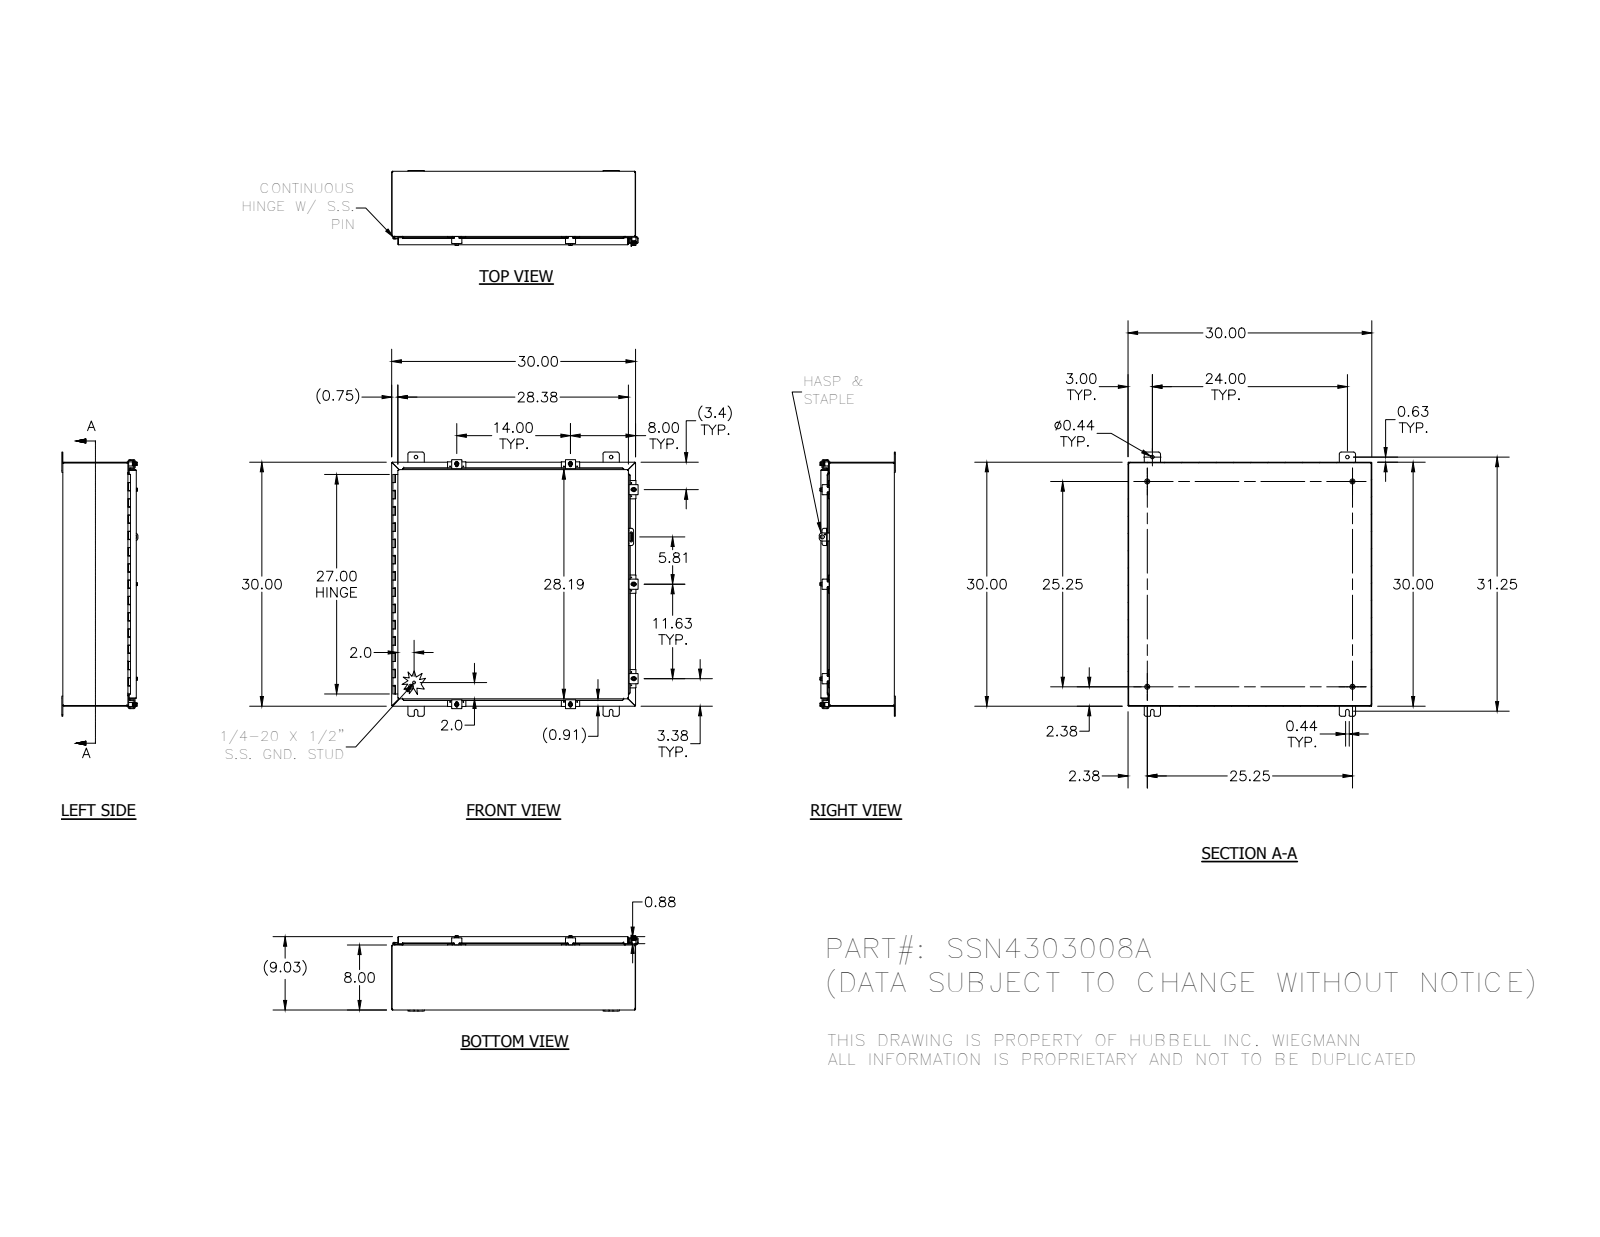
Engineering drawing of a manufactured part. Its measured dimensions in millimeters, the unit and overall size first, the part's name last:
Units: millimetres
Overall size (bounding box): 825.5 × 767.5 × 237.6
Round holes (diameter × count): ⌀2.8 ×14, ⌀5.4 ×7, ⌀7.1 ×7, ⌀7.6 ×7, ⌀11.1 ×4, ⌀3.2 ×1, ⌀4 ×1, ⌀12.7 ×1
Round bosses / shafts (diameter × count): ⌀6.4 ×9, ⌀13.2 ×7, ⌀12.7 ×7, ⌀8.9 ×7, ⌀15.9 ×4, ⌀8.4 ×4, ⌀8.6 ×1, ⌀3 ×1
Partial cylindrical surfaces — rounded edges, fillets, slot ends (radius × count): R0.8 ×83, R3.2 ×37, R6.4 ×33, R0.8 ×23, R2.7 ×23, R1.6 ×18, R3.6 ×14, R2.5 ×10
Main face-to-face distances: 1.9, 227.6, 760.1, 225.7, 229.4, 762, 758.2, 201.3, 26.2, 203.2
Hole centre spacings: 22.3, 744.2, 355.6, 41.3, 295.3, 316, 335.1, 376.3
Volume: 4 010 000 mm³ · Surface area: 4 157 000 mm²
Bodies: 52 solids, 2090 faces (818 planar, 905 cylindrical, 367 other)
Part name (STEP PRODUCT): 28x28; 32874-30P; SSN43030ALID; 38412 (+8 more)
STEP written by: SolidWorks 2014 (AUTOMOTIVE_DESIGN)
